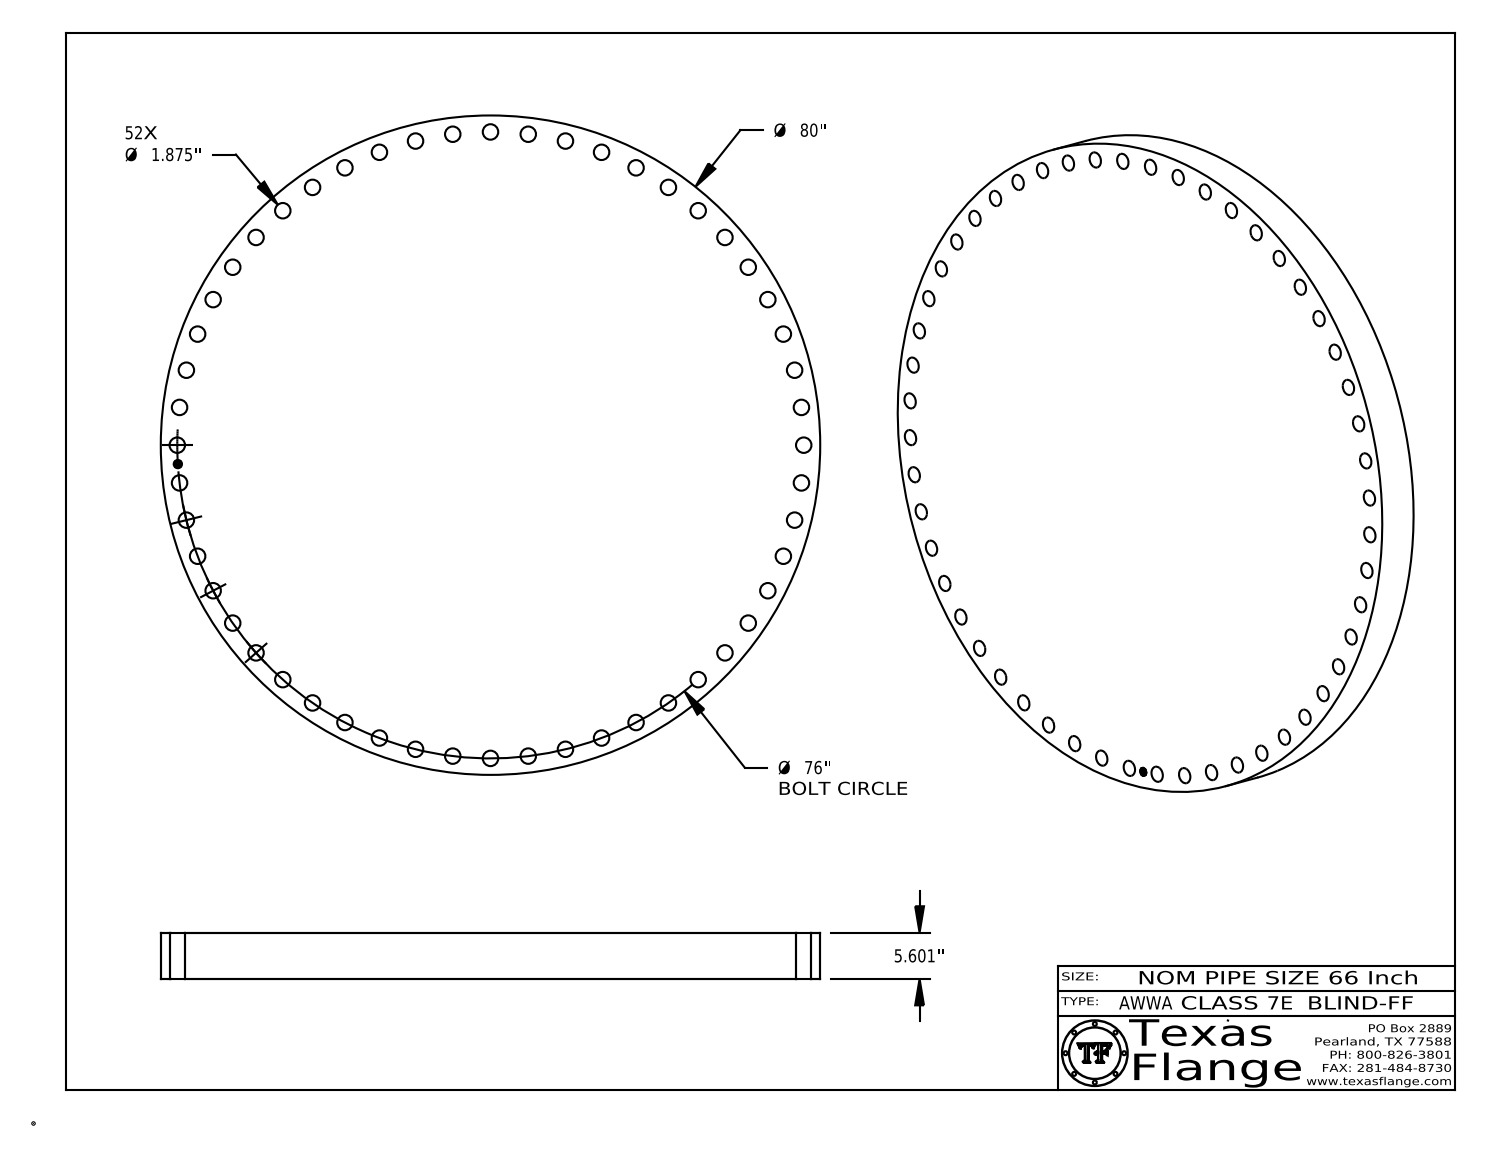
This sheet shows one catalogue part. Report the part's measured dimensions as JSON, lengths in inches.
{"part_name": "AWWA Class 7E-BLIND-FF", "step_written_by": "CATIA V5 STEP AP214 (AUTOMOTIVE_DESIGN)", "units": "inches", "bodies": {"solids": 1, "faces": 493, "planar": 367, "cylindrical": 126, "other": 0}, "overall_size": [80, 80, 5.601], "volume_in3": 27349, "surface_area_in2": 12889, "round_holes": [[1.875, 52], [1, 1]], "round_bosses_or_shafts": [[0.061, 8], [80, 1], [0.788, 1]], "face_to_face_distances": [5.601, 0.015, 5.586, 0.298, 0.293, 0.019, 0.054, 0.193, 0.248, 0.044], "hole_center_spacings": [26.95, 31.191, 22.61, 4.589, 35.319, 39.318, 18.188, 46.87]}
